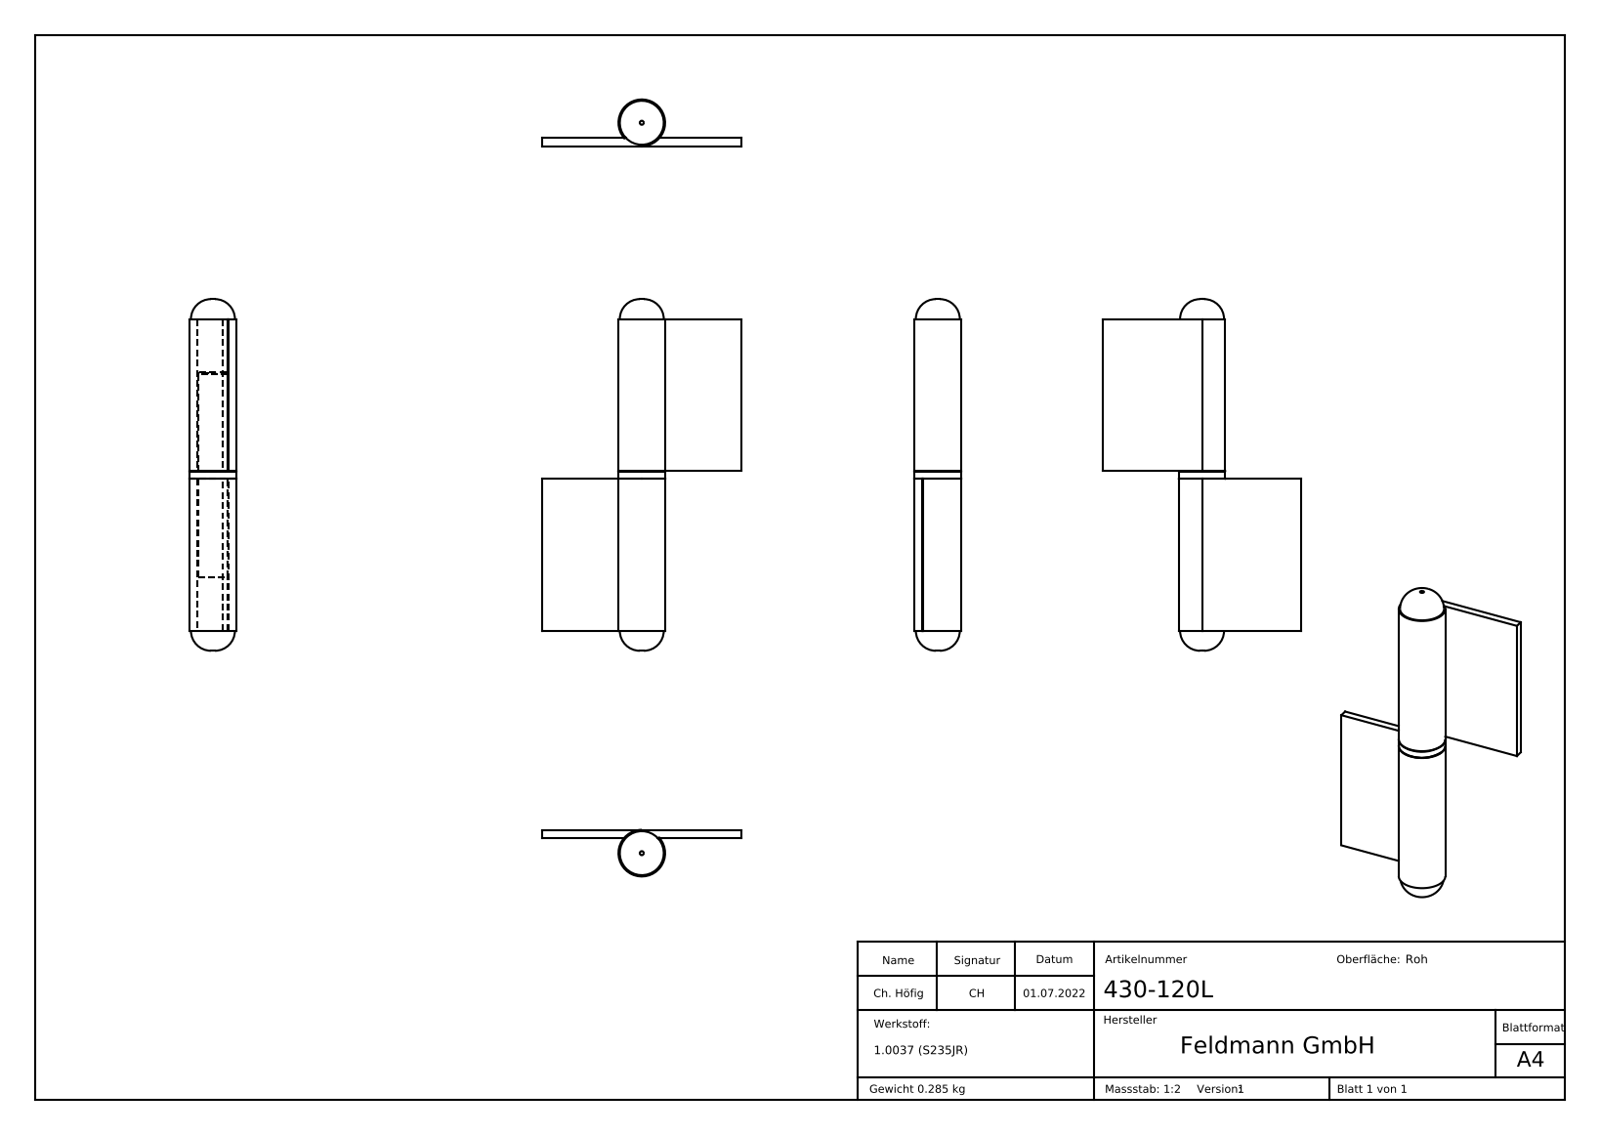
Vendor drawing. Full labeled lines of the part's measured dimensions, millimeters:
Part name (STEP PRODUCT): 430-120L; 430-xxL Teil1_430-120L Teil1; 430-xxL Teil2_430-120L Teil2
STEP written by: SolidWorks 2018 (CONFIG_CONTROL_DESIGN)
Units: millimetres
Bodies: 3 solids, 232 faces (134 planar, 7 cylindrical, 91 other)
Overall size (bounding box): 132 × 74.5 × 17.5
Volume: 36 512 mm³ · Surface area: 23 132 mm²
Round holes (diameter × count): ⌀11.5 ×1
Round bosses / shafts (diameter × count): ⌀17.5 ×1, ⌀11.3 ×1
Main face-to-face distances: 3, 57, 60, 117, 20, 97, 37, 40, 74.5, 77
